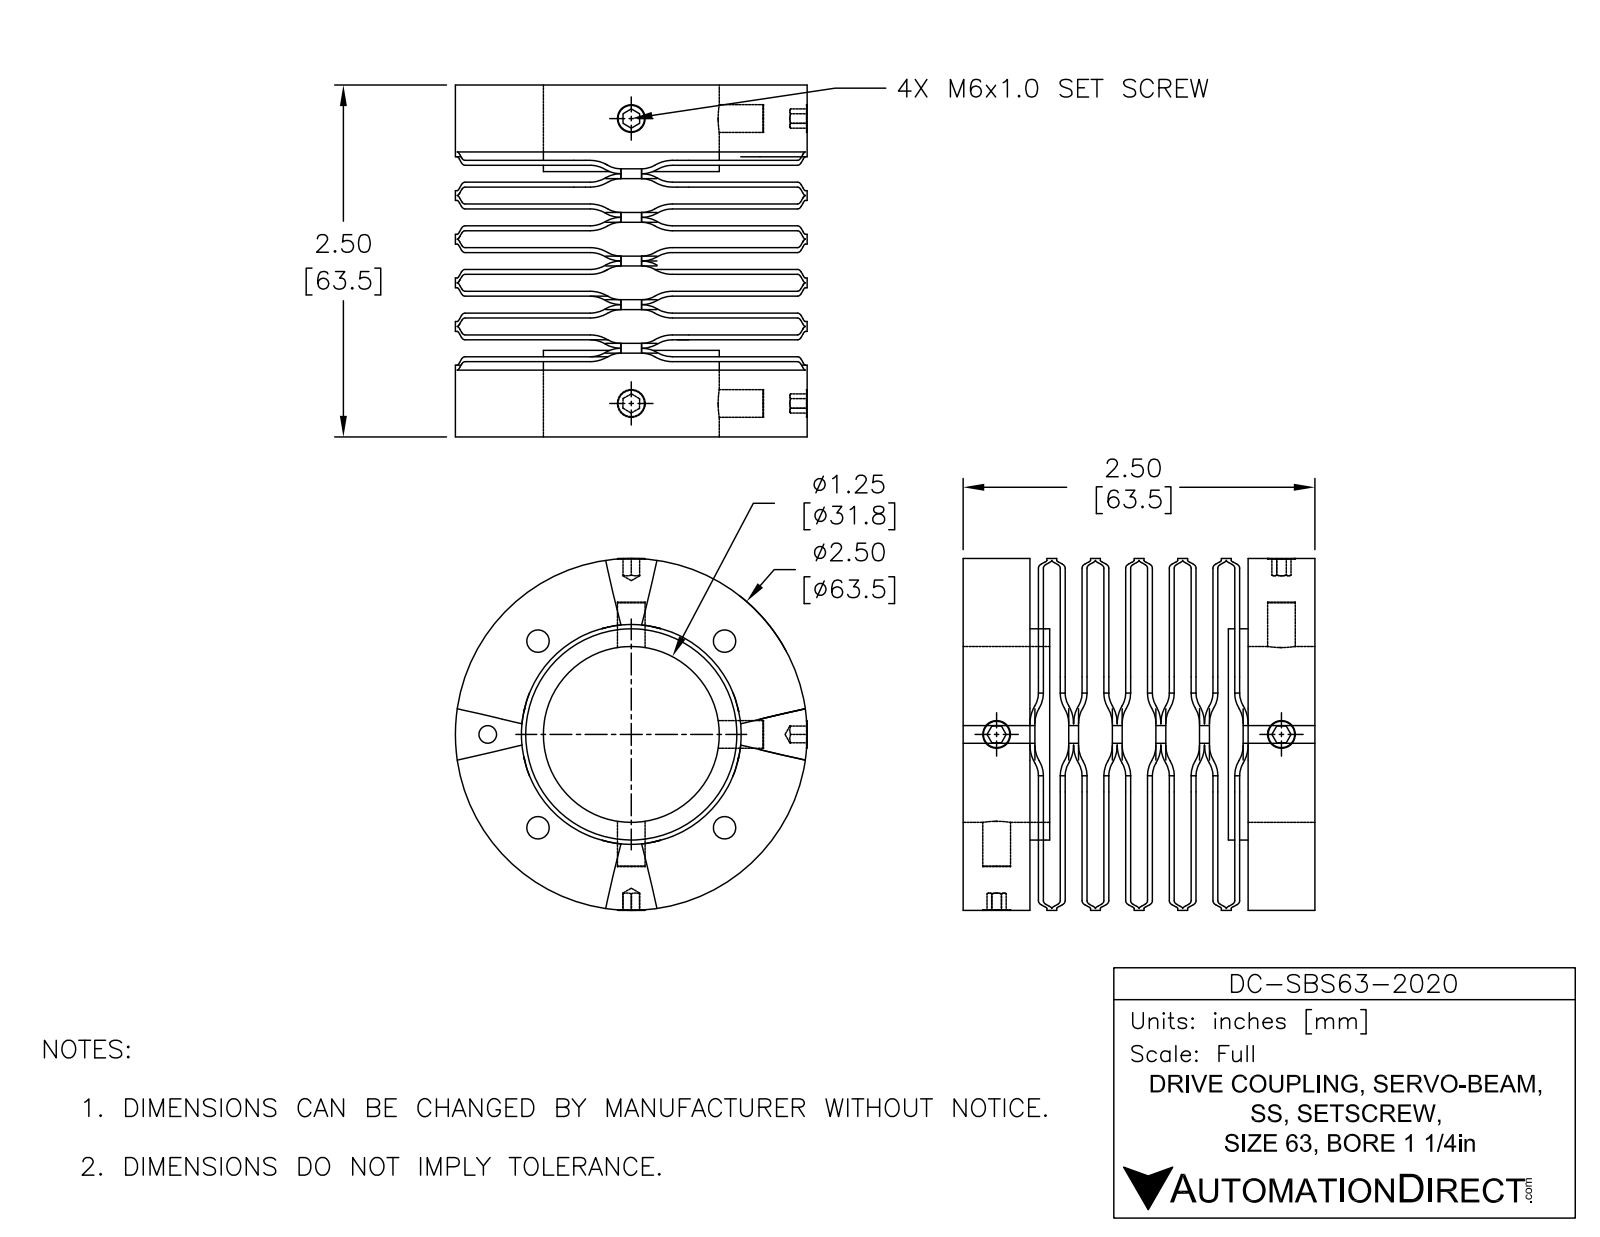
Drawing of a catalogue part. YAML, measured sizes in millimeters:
part_name: "DC-SBS63-2020"
step_written_by: "SolidWorks 2015 (AUTOMOTIVE_DESIGN)"
units: millimeters
bodies: {solids: 16, faces: 795, planar: 359, cylindrical: 428, other: 8}
overall_size: [63.54, 63.5, 63.5]
volume: 79943
surface_area: 64267
round_holes:
  - {diameter: 4.04, count: 4}
  - {diameter: 5.2, count: 4}
  - {diameter: 3.17, count: 1}
  - {diameter: 31.75, count: 1}
  - {diameter: 39.67, count: 1}
round_bosses_or_shafts:
  - {diameter: 6.05, count: 4}
  - {diameter: 63.5, count: 1}
  - {diameter: 38.1, count: 1}
partial_cylinders:
  - {radius: 1.8, count: 320}
face_to_face_distances: [7.88, 15.76, 23.64, 3.95, 0.89, 4.84, 3.93, 8.77, 12.72, 3.04]
hole_center_spacings: [23.82, 33.68, 19.13, 45.95, 47.63, 25.91, 51.02]
